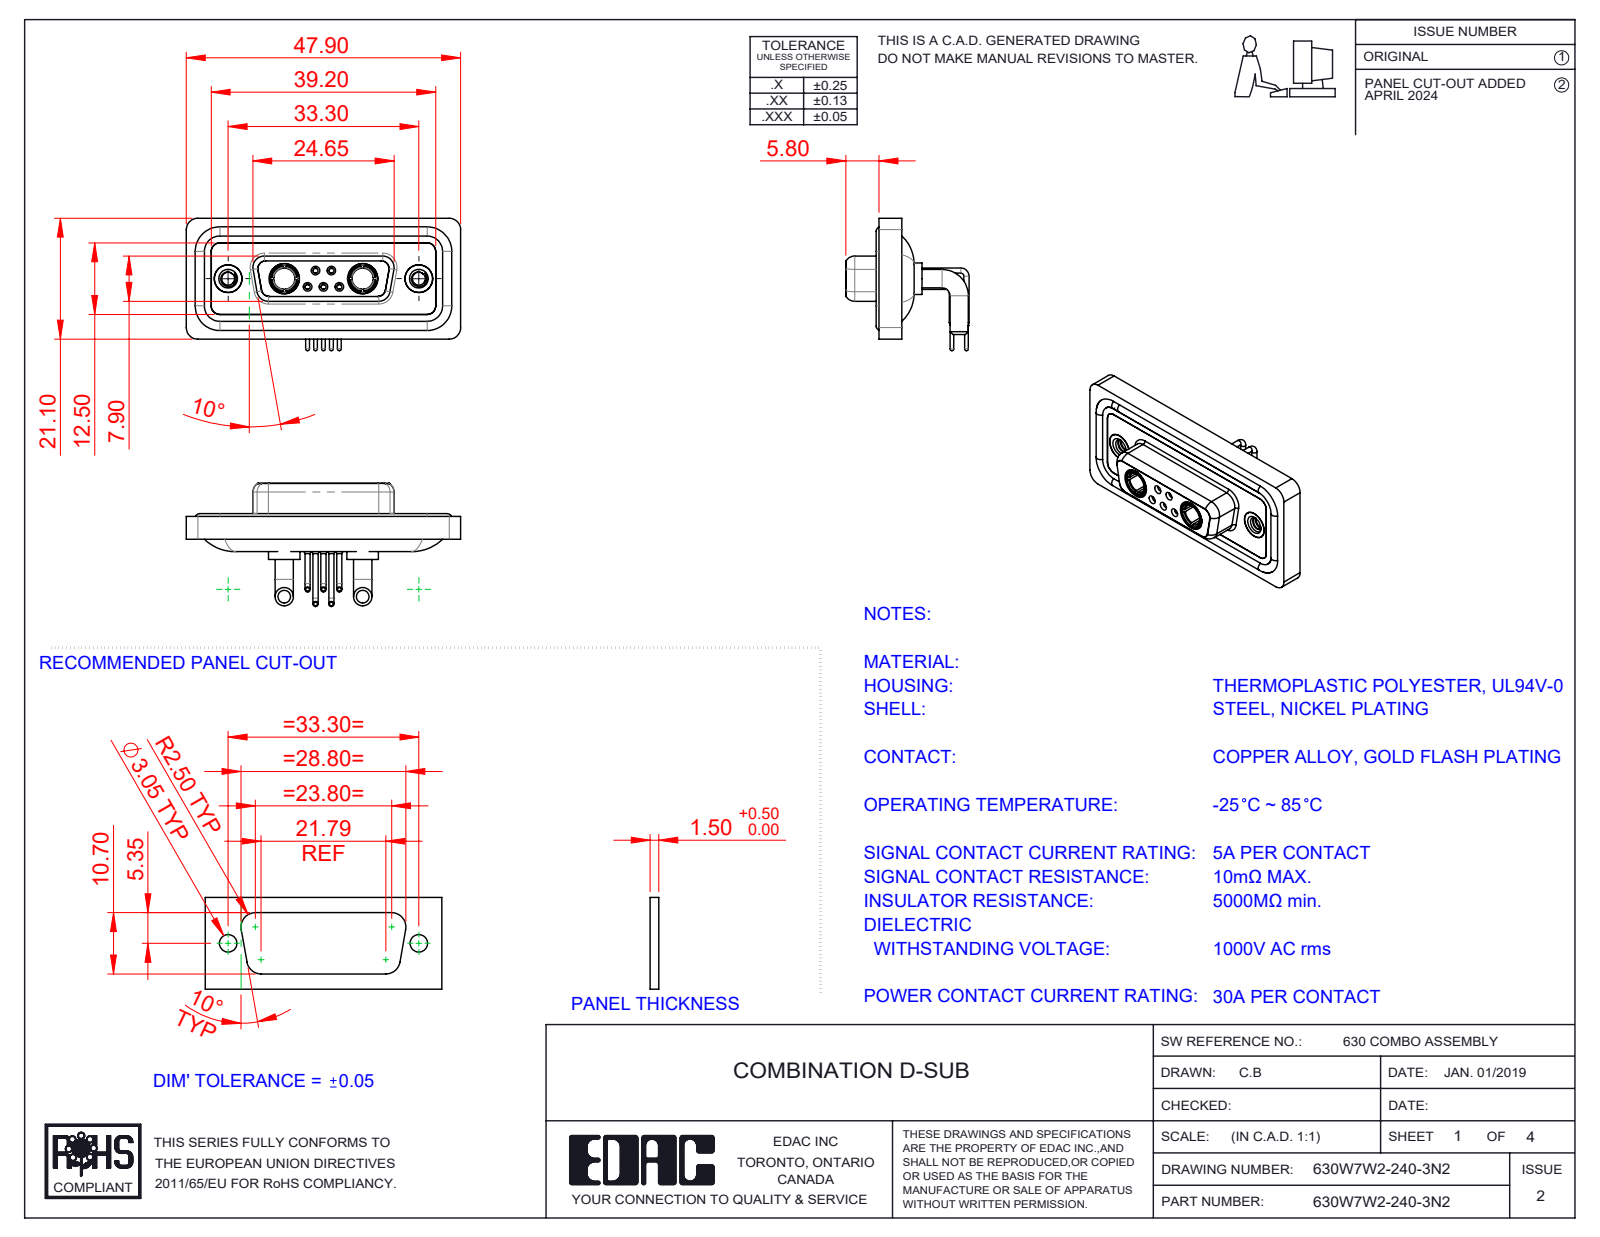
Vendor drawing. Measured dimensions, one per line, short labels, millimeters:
name: 630Combo Contact Row 2_50 Contacts; 630Combo Housing_7W2; 630W7W2-140-3N2; 630Combo Shell Front_15 Contacts (+5 more)
written by: SolidWorks 2023 (CONFIG_CONTROL_DESIGN)
unit: mm
bodies: 16 solids, 807 faces (238 planar, 353 cylindrical, 216 other)
size: 47.9 × 23.12 × 21.53
volume: 6 252 mm³; area: 10 242 mm²
holes: 5× ⌀0.9, 5× ⌀1.1, 5× ⌀1.5, 5× ⌀2, 4× ⌀4.85, 3× ⌀1.6, 2× ⌀1.7, 2× ⌀2.26, 2× ⌀3.7, 2× ⌀4, 2× ⌀4.05, 2× ⌀5
bosses: 6× ⌀1.6, 5× ⌀0.9, 5× ⌀0.65, 4× ⌀3.2, 2× ⌀5.5, 2× ⌀5.2, 2× ⌀4.96, 2× ⌀4.95
rounds: 20× R2, 18× R1.5, 12× R1.35, 8× R1.6, 4× R0.25, 4× R0.5, 4× R0.6, 4× R0.65
face distances: 0.4, 1.8, 1.1, 1.6, 2.5, 2.9, 3.1, 3.7, 4.1, 1.5
hole spacings: 3.16, 2.77, 9.8, 23.5, 4.31, 4.33, 5.03, 5.04
